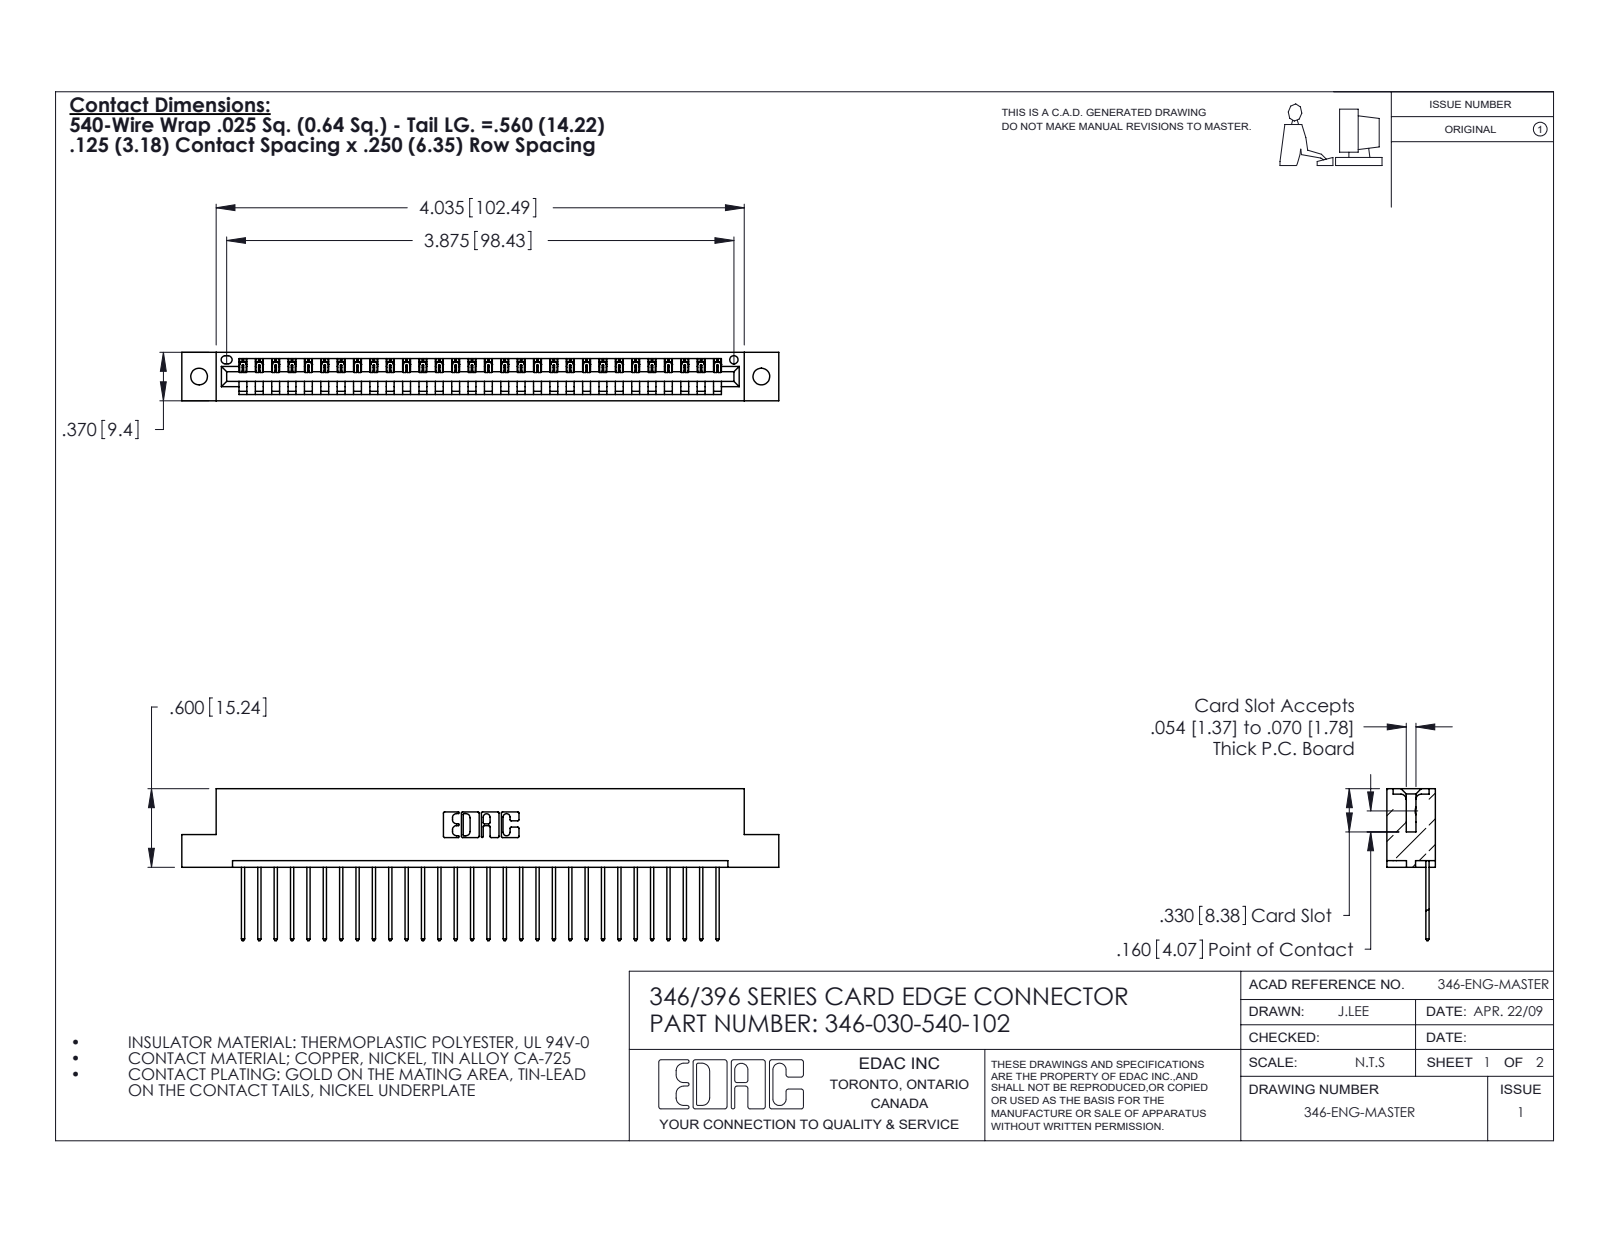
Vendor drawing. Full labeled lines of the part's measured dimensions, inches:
Part name (STEP PRODUCT): 345-292-001_345-293-140; 346 Part_Flush Mounting Lugs - 0.128 Dia; 346-030-540-102
STEP written by: SolidWorks 2020 (CONFIG_CONTROL_DESIGN)
Units: inches
Bodies: 31 solids, 1862 faces (1276 planar, 586 cylindrical, 0 other)
Overall size (bounding box): 4.56 × 1.16 × 0.37
Volume: 0.672 in³ · Surface area: 21.16 in²
Round holes (diameter × count): ⌀0.128 ×2, ⌀0.064 ×1
Partial cylindrical surfaces — rounded edges, fillets, slot ends (radius × count): R0.006 ×60, R0.01 ×60, R0.01 ×22, R0.007 ×6, R0.031 ×6, R0.026 ×3, R0.031 ×2, R0.04 ×2
Main face-to-face distances: 0.048, 0.322, 0.37, 0.25, 0.072, 0.298, 0.025, 0.148, 0.222, 0.1
Hole centre spacings: 0.246, 4.087, 4.295
